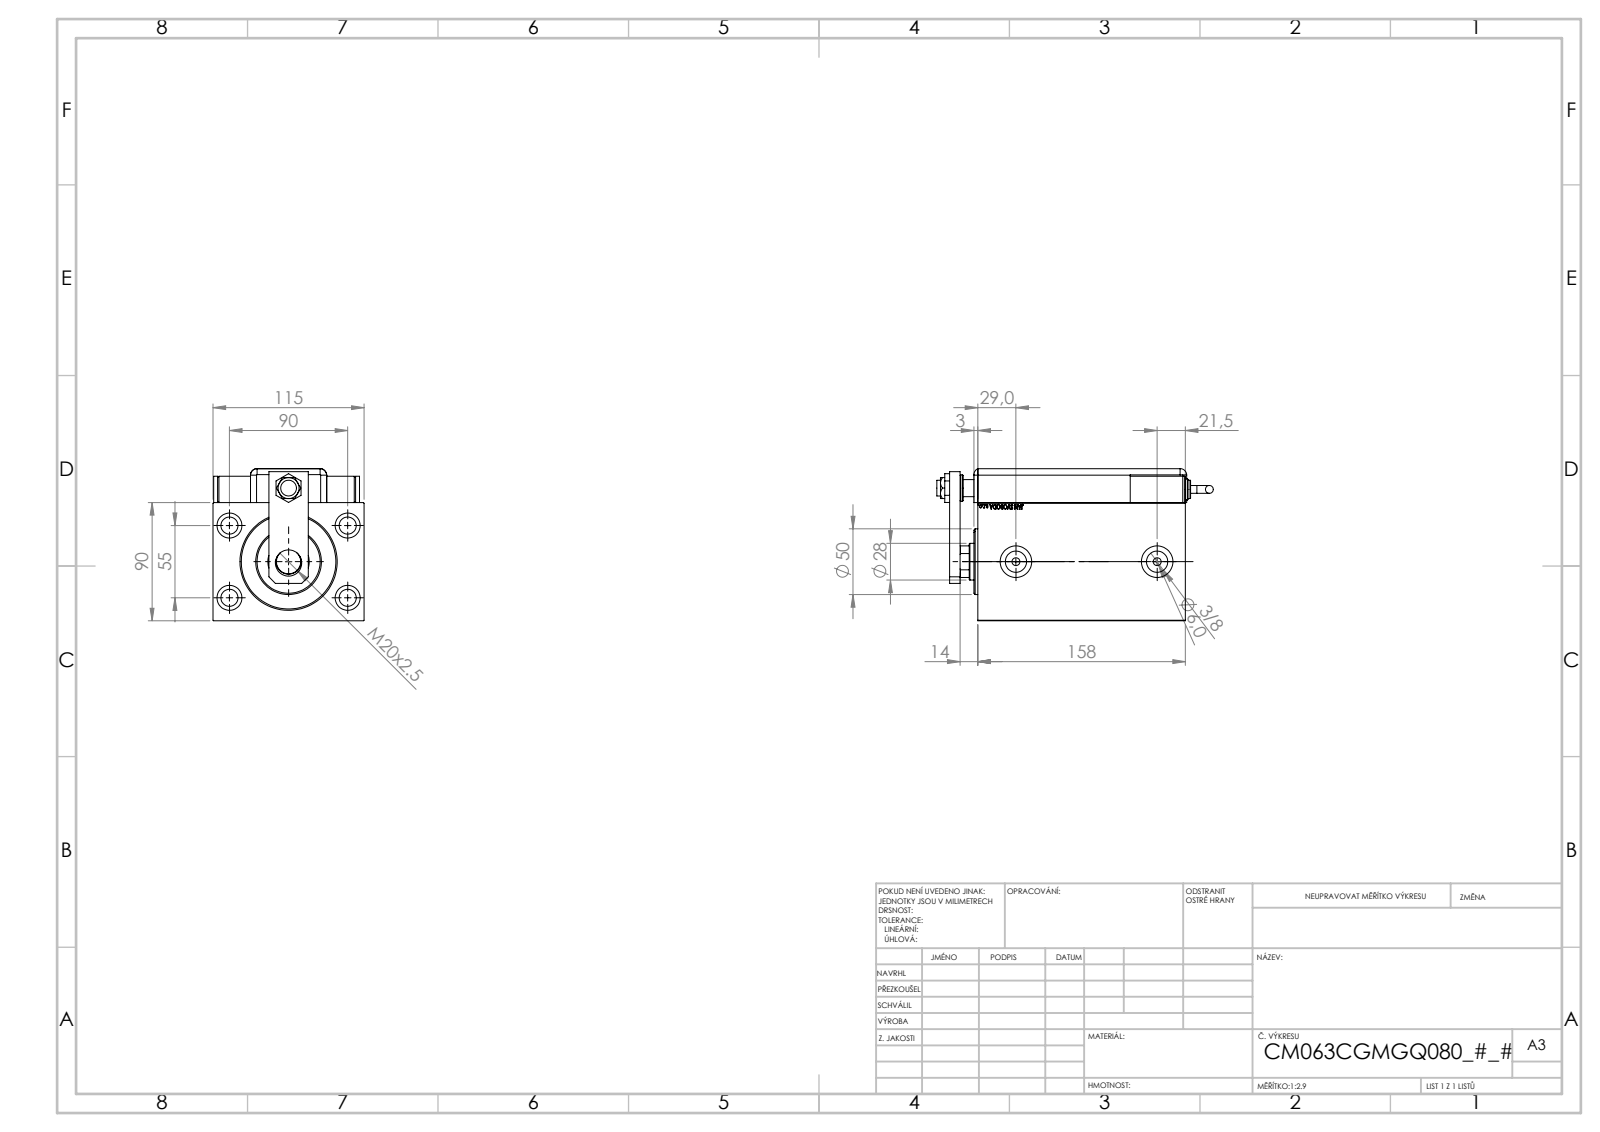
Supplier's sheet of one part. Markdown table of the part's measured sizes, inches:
| quantity | value |
| --- | --- |
| part name | NUT_D19; V450CM_C_VCP; ZARAZKA_Q; V450CM_VC_B (+7 more) |
| STEP written by | SolidWorks 2019 (CONFIG_CONTROL_DESIGN) |
| units | inches |
| bodies | 13 solids, 1249 faces (615 planar, 117 cylindrical, 517 other) |
| overall size | 8.286 × 4.559 × 4.528 |
| volume | 91.84 in³ |
| surface area | 391.4 in² |
| round holes (diameter × count) | 0.512 × 5, 0.748 × 4, 0.157 × 2, 0.236 × 2, 0.315 × 2, 0.637 × 2, 0.945 × 2, 0.472 × 1, 0.551 × 1, 0.728 × 1, 0.787 × 1, 1.102 × 1 |
| round bosses / shafts (diameter × count) | 0.787 × 3, 0.63 × 2, 0.551 × 2, 0.236 × 2, 1.969 × 1 |
| partial cylindrical surfaces (radius × count) | 0.197 × 9, 0.394 × 1, 0.531 × 1 |
| main face-to-face distances | 3.543, 0.118, 4.528, 6.22, 1.016, 4.559, 0.689, 5.531, 1.122, 4.441 |
| hole center spacings | 2.076, 2.097, 2.056, 2.165, 3.543, 3.734, 4.153, 0.039 |
